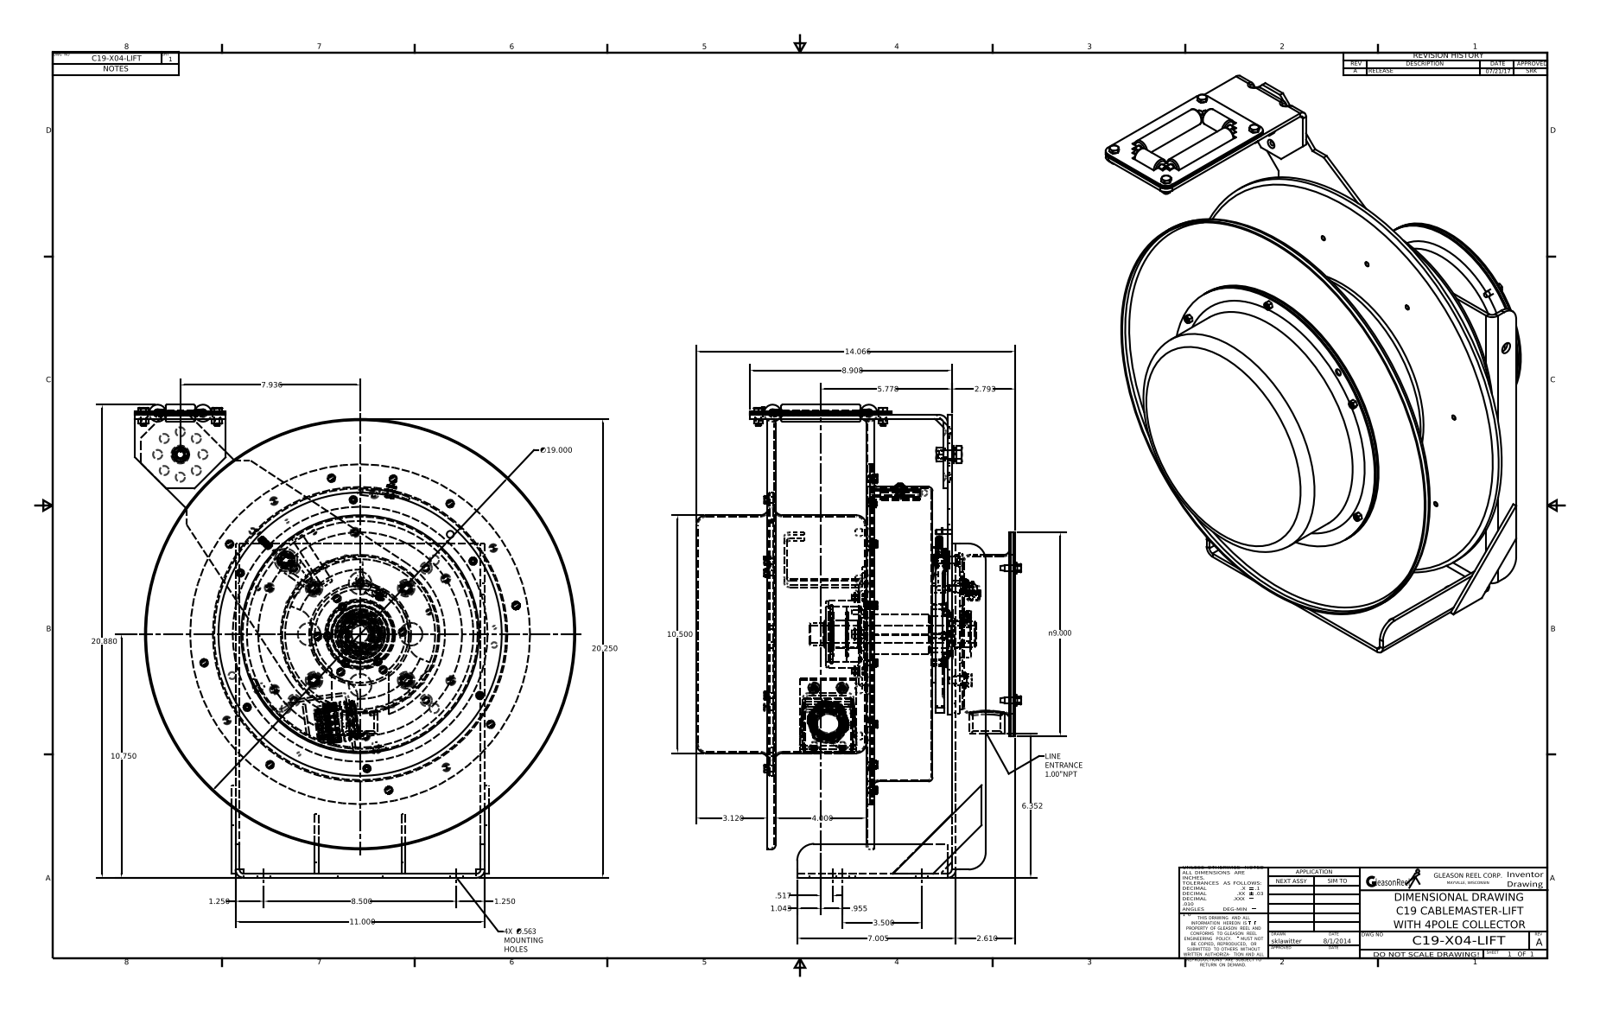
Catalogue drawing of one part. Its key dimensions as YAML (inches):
part_name: "C19-X04-LIFT (SW)"
step_written_by: "Autodesk Inventor 2016 (AUTOMOTIVE_DESIGN)"
units: inches
bodies: {solids: 173, faces: 3480, planar: 1373, cylindrical: 1017, other: 1090}
overall_size: [20.88, 19.437, 14.33]
volume: 233.7
surface_area: 4867
round_holes:
  - {diameter: 0.25, count: 31}
  - {diameter: 0.197, count: 30}
  - {diameter: 0.163, count: 26}
  - {diameter: 0.219, count: 14}
  - {diameter: 0.406, count: 13}
  - {diameter: 0.422, count: 12}
  - {diameter: 0.156, count: 7}
  - {diameter: 0.281, count: 7}
  - {diameter: 0.199, count: 6}
  - {diameter: 0.211, count: 6}
  - {diameter: 0.224, count: 6}
  - {diameter: 1, count: 6}
round_bosses_or_shafts:
  - {diameter: 0.197, count: 30}
  - {diameter: 0.236, count: 10}
  - {diameter: 0.405, count: 6}
  - {diameter: 0.394, count: 6}
  - {diameter: 0.191, count: 6}
  - {diameter: 0.5, count: 5}
  - {diameter: 0.457, count: 5}
  - {diameter: 0.315, count: 5}
partial_cylinders:
  - {radius: 0.03, count: 67}
  - {radius: 0.01, count: 64}
  - {radius: 0.015, count: 41}
  - {radius: 0.078, count: 18}
  - {radius: 0.006, count: 12}
  - {radius: 0.06, count: 12}
  - {radius: 0.124, count: 8}
  - {radius: 0.125, count: 7}
face_to_face_distances: [0.06, 0.185, 0.179, 0.245, 0.125, 4.305, 4.12, 4.06, 2.687, 2.872]
hole_center_spacings: [1.25, 0.765, 1, 1.414, 1.848, 4.063, 5.443, 5.446]
